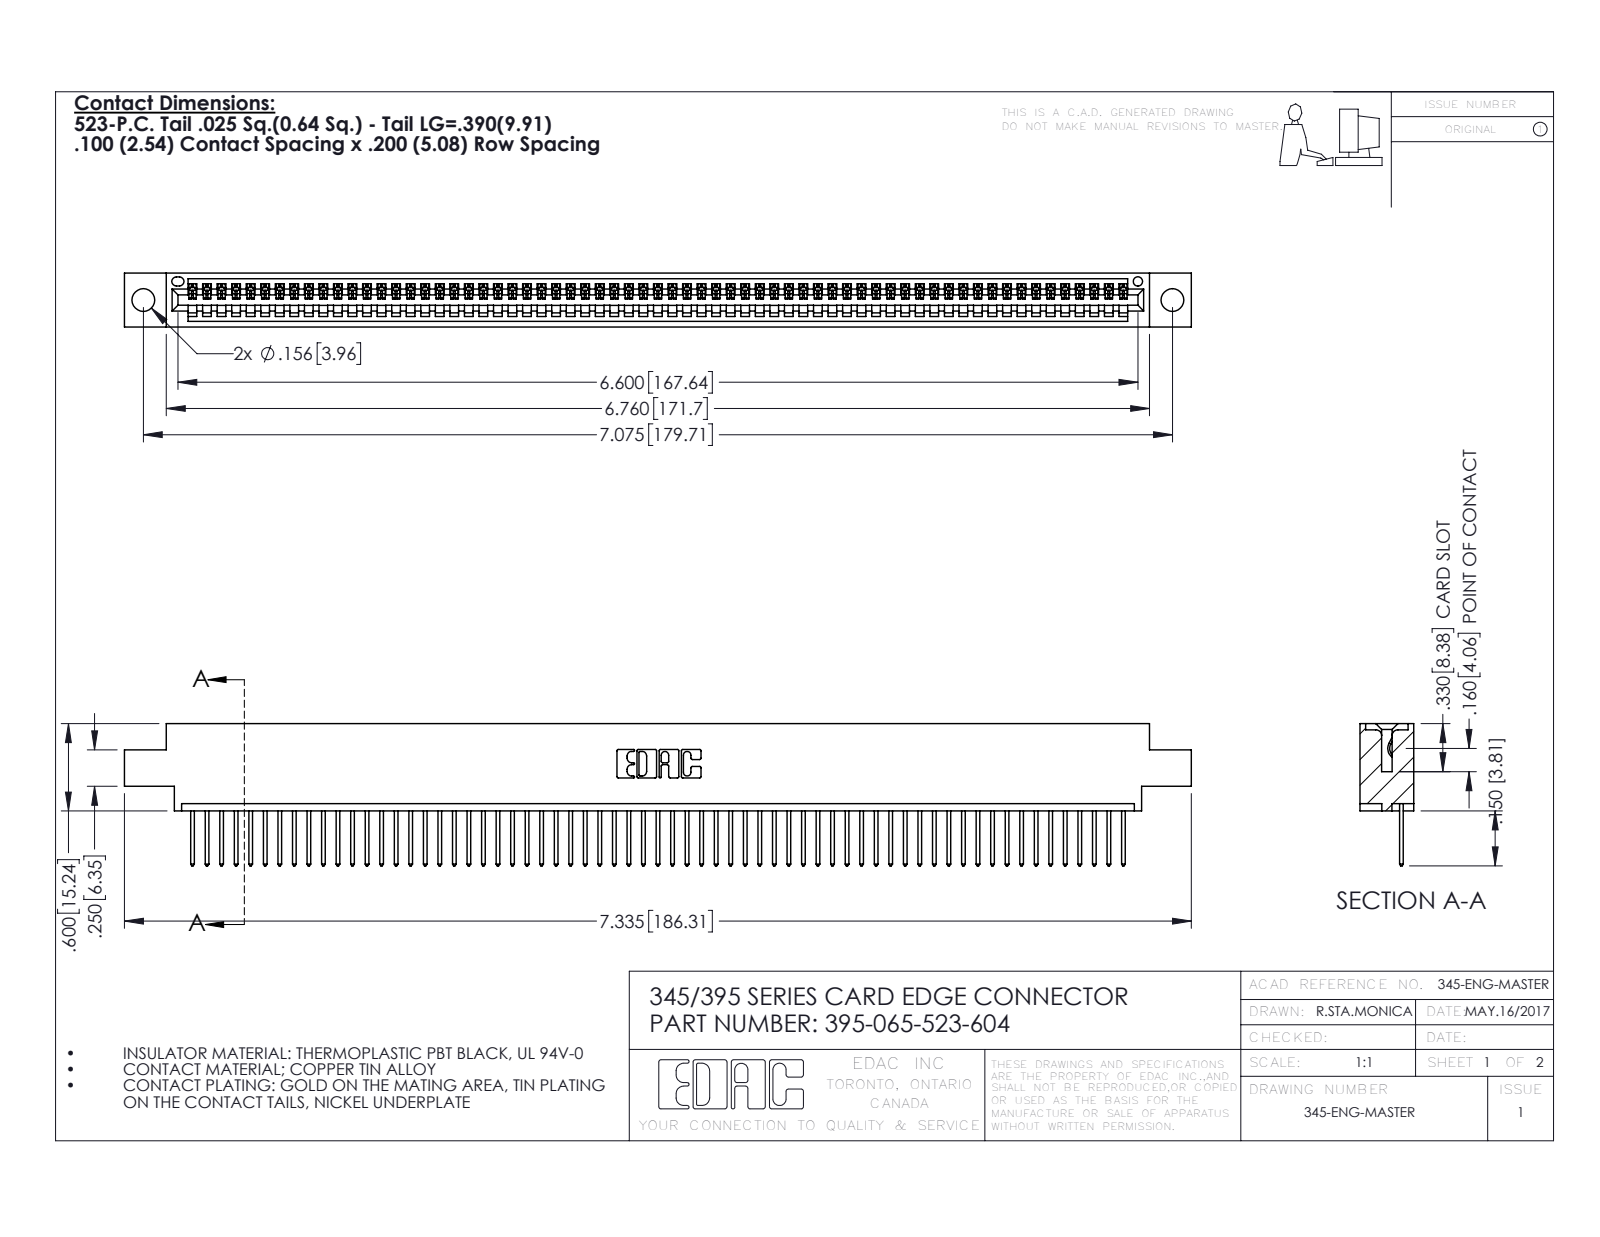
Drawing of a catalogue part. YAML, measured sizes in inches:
part_name: "345 Part_0.170 Offset - 0.156 Dia-TH; 345-292-001_345-293-123; 395-065-523-604"
step_written_by: "SolidWorks 2016 (CONFIG_CONTROL_DESIGN)"
units: inches
bodies: {solids: 66, faces: 3900, planar: 2684, cylindrical: 1216, other: 0}
overall_size: [7.335, 0.977, 0.37]
volume: 1.078
surface_area: 36.87
round_holes:
  - {diameter: 0.156, count: 2}
  - {diameter: 0.064, count: 1}
partial_cylinders:
  - {radius: 0.006, count: 130}
  - {radius: 0.01, count: 130}
  - {radius: 0.01, count: 22}
  - {radius: 0.007, count: 6}
  - {radius: 0.031, count: 6}
  - {radius: 0.026, count: 3}
  - {radius: 0.031, count: 2}
  - {radius: 0.04, count: 2}
face_to_face_distances: [0.298, 0.072, 0.37, 0.098, 0.272, 0.025, 0.2, 0.225, 0.175, 0.149]
hole_center_spacings: [0.27, 6.839, 7.075]
